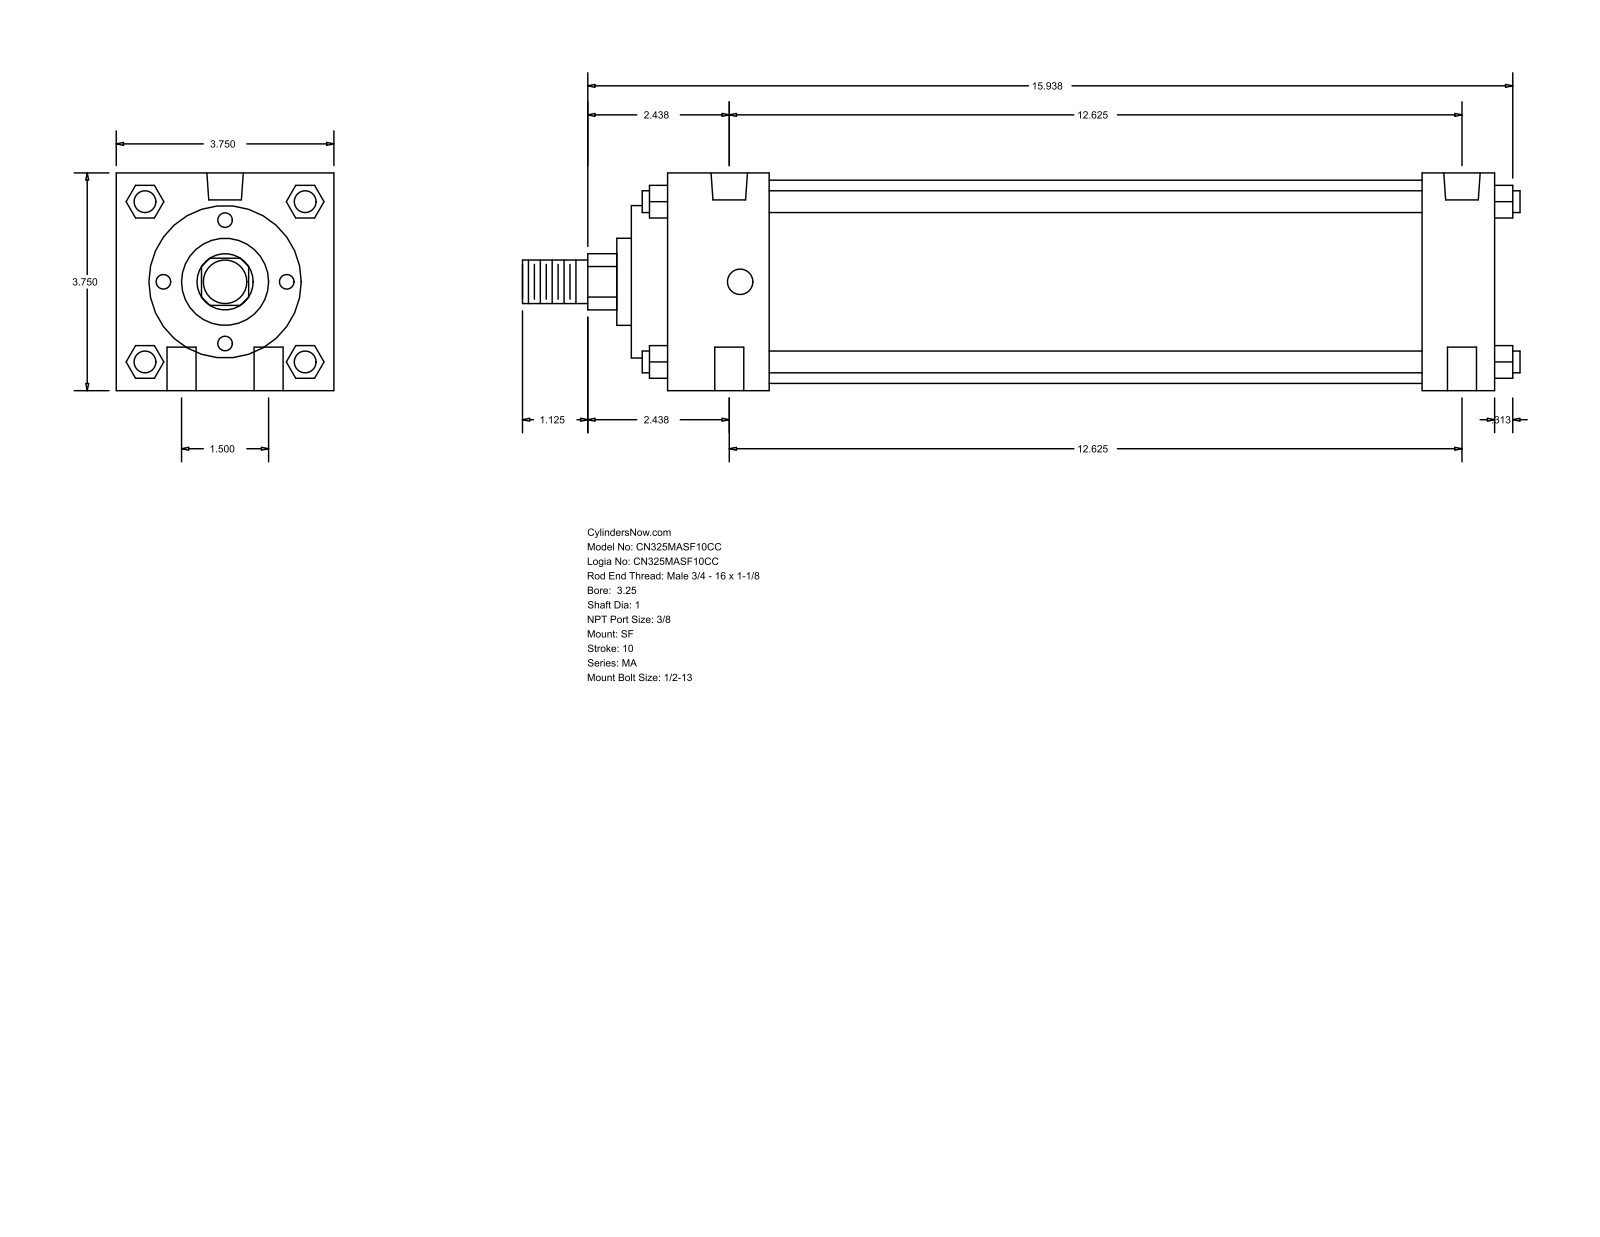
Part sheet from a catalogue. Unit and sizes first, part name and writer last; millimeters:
Units: millimetres
Overall size (bounding box): 436.56 × 95.25 × 95.25
Round holes (diameter × count): ⌀12.7 ×4, ⌀11.11 ×2, ⌀15.93 ×2
Round bosses / shafts (diameter × count): ⌀9.53 ×4, ⌀88.9 ×1, ⌀66.67 ×1, ⌀38.1 ×1, ⌀25.4 ×1, ⌀19.05 ×1
Partial cylindrical surfaces — rounded edges, fillets, slot ends (radius × count): R12.29 ×1
Main face-to-face distances: 95.24, 361.96, 330.2, 31.76, 44.46, 285.74, 317.5, 15.87, 60.33, 346.07
Hole centre spacings: 19.05, 321.25, 320.68, 38.1, 322.94, 311.15
Bodies: 0 solids, 126 faces (95 planar, 31 cylindrical, 0 other)
Part name (STEP PRODUCT): MA_SF__0325_1
STEP written by: GSSL Pune (CONFIG_CONTROL_DESIGN)
